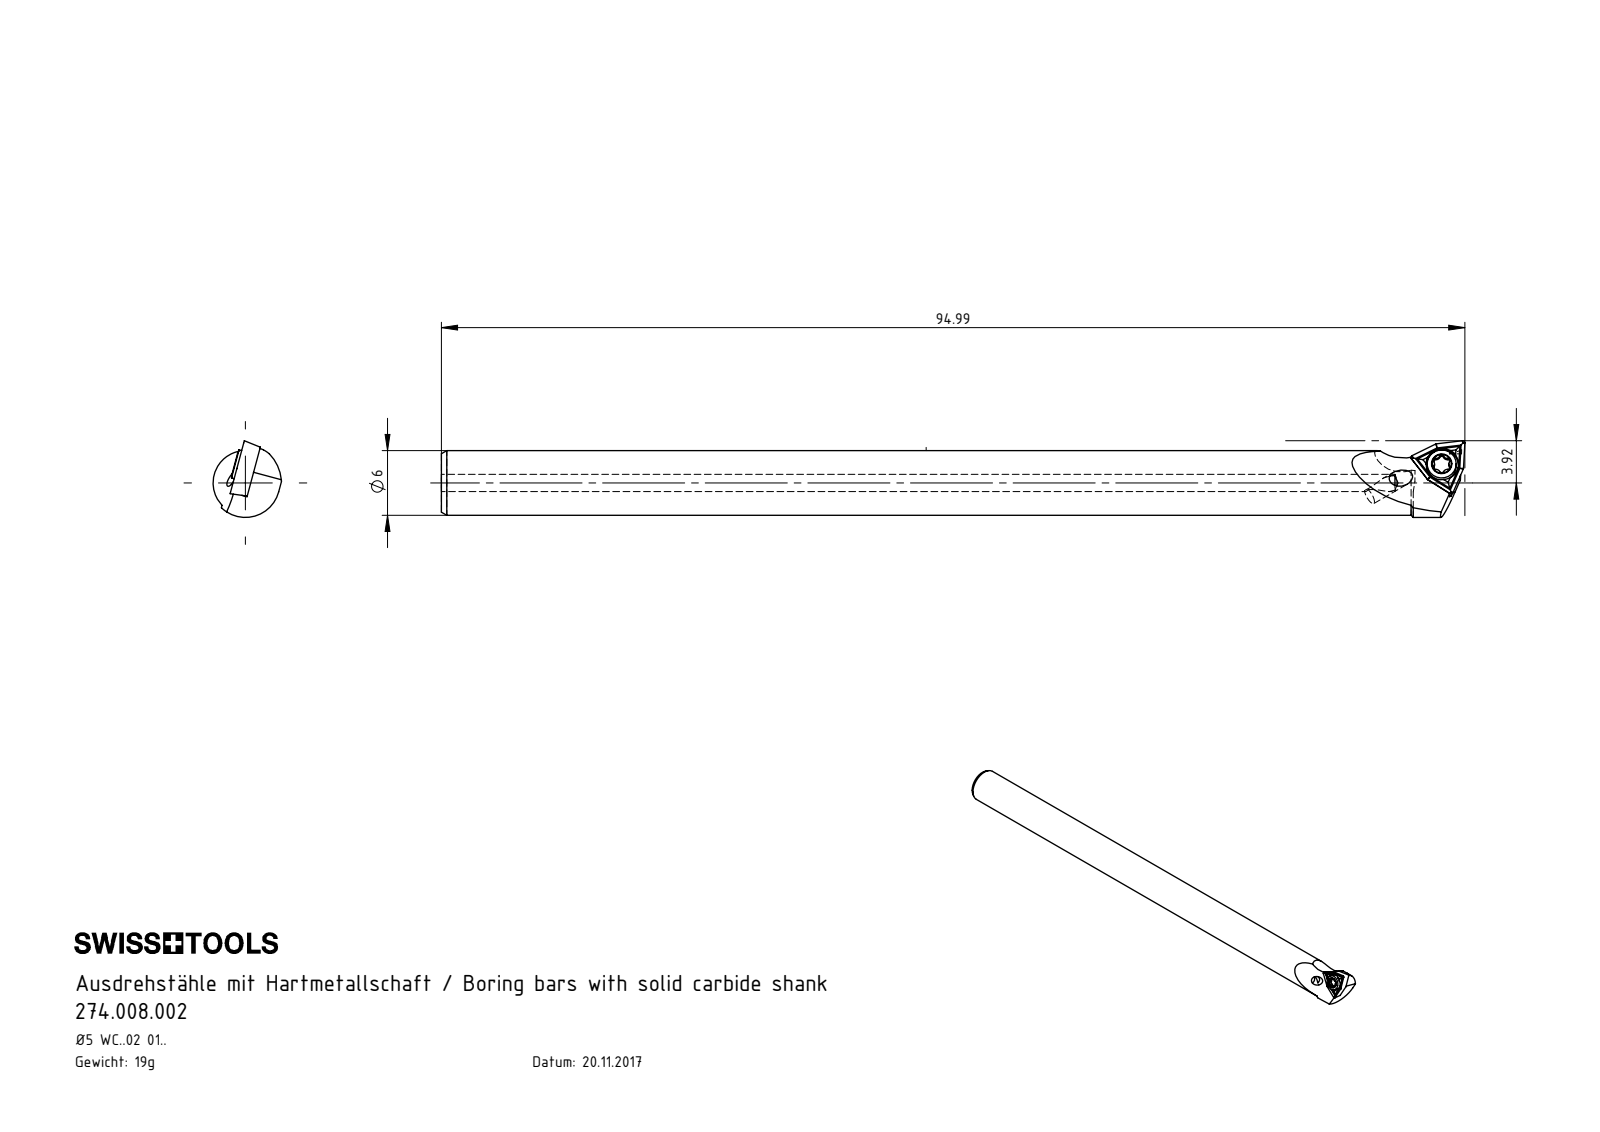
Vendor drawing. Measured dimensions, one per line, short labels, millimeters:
name: SFS-Torx-M2; WCMT020102; B08-WWA.K11.100_A; B08-WWA.K11.100
written by: SolidWorks 2015 (AUTOMOTIVE_DESIGN)
unit: mm
bodies: 3 solids, 108 faces (38 planar, 33 cylindrical, 37 other)
size: 96.28 × 7.32 × 7
volume: 3 412 mm³; area: 2 692 mm²
holes: 2× ⌀1.6, 1× ⌀2.3, 1× ⌀3
bosses: 1× ⌀7, 1× ⌀2.7, 1× ⌀2
rounds: 6× R0.21, 6× R0.36, 2× R0.8
face distances: 1.49, 1.39, 1.61, 3, 3.1, 3.2, 1.59, 3.5, 1.89, 0.5
